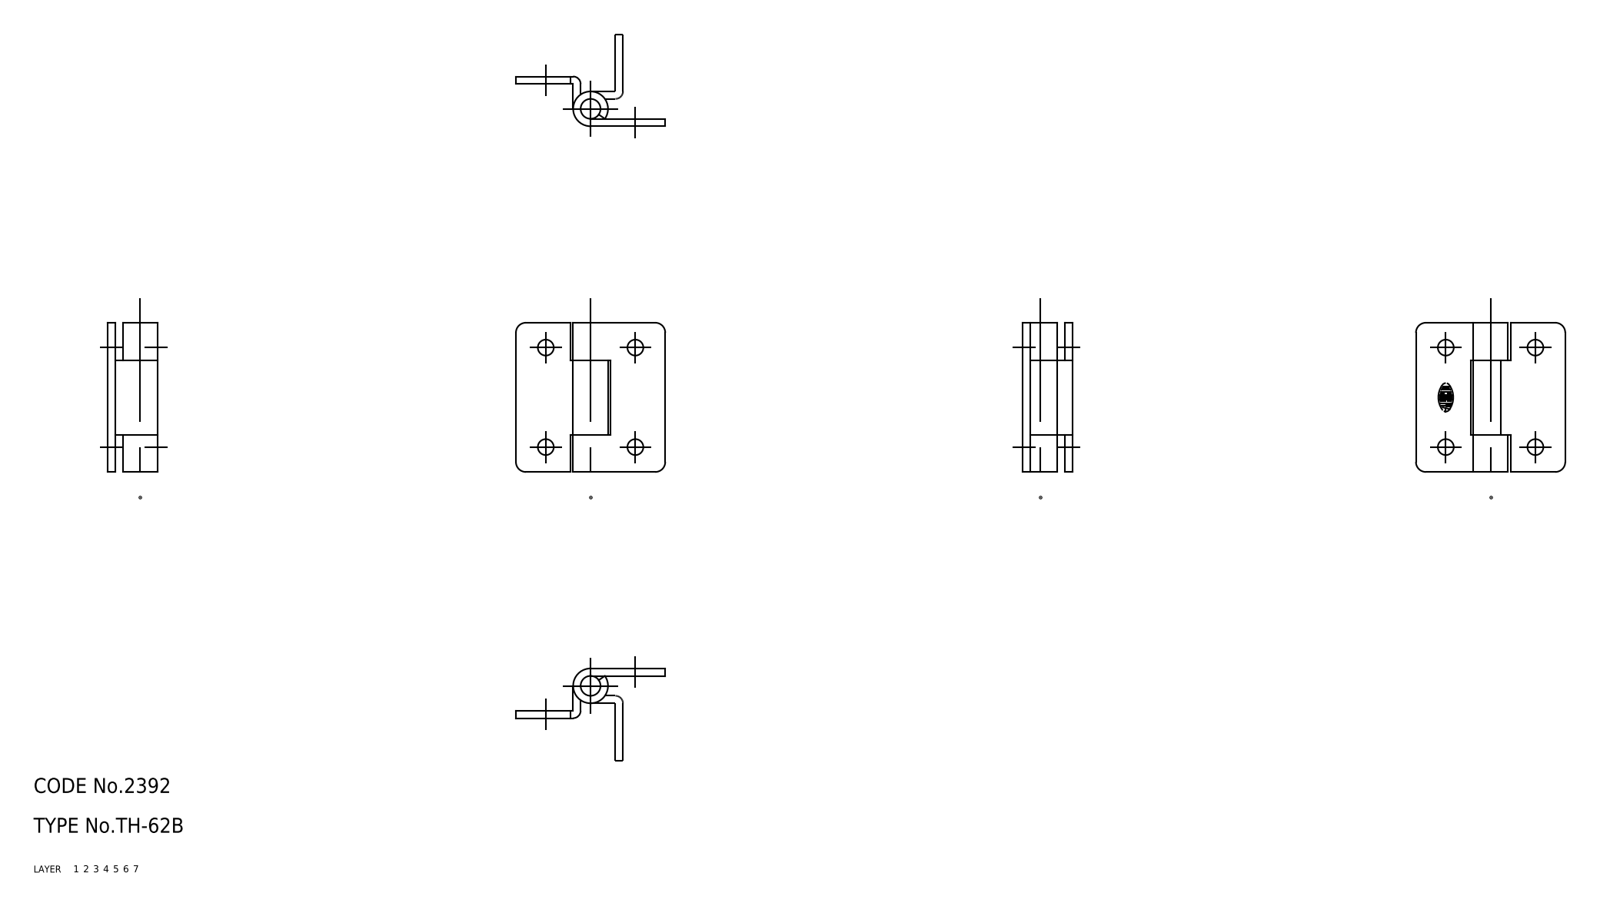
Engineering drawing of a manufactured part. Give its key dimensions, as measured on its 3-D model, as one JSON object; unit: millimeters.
{"part_name": "shaft; hinge piece_B; hinge piece_A; TH_62B_13075_36", "step_written_by": "CADfix (AUTOMOTIVE_DESIGN)", "units": "millimeters", "bodies": {"solids": 3, "faces": 45, "planar": 0, "cylindrical": 0, "other": 45}, "overall_size": [30, 30, 10], "volume_mm3": 2211, "surface_area_mm2": 3323}
